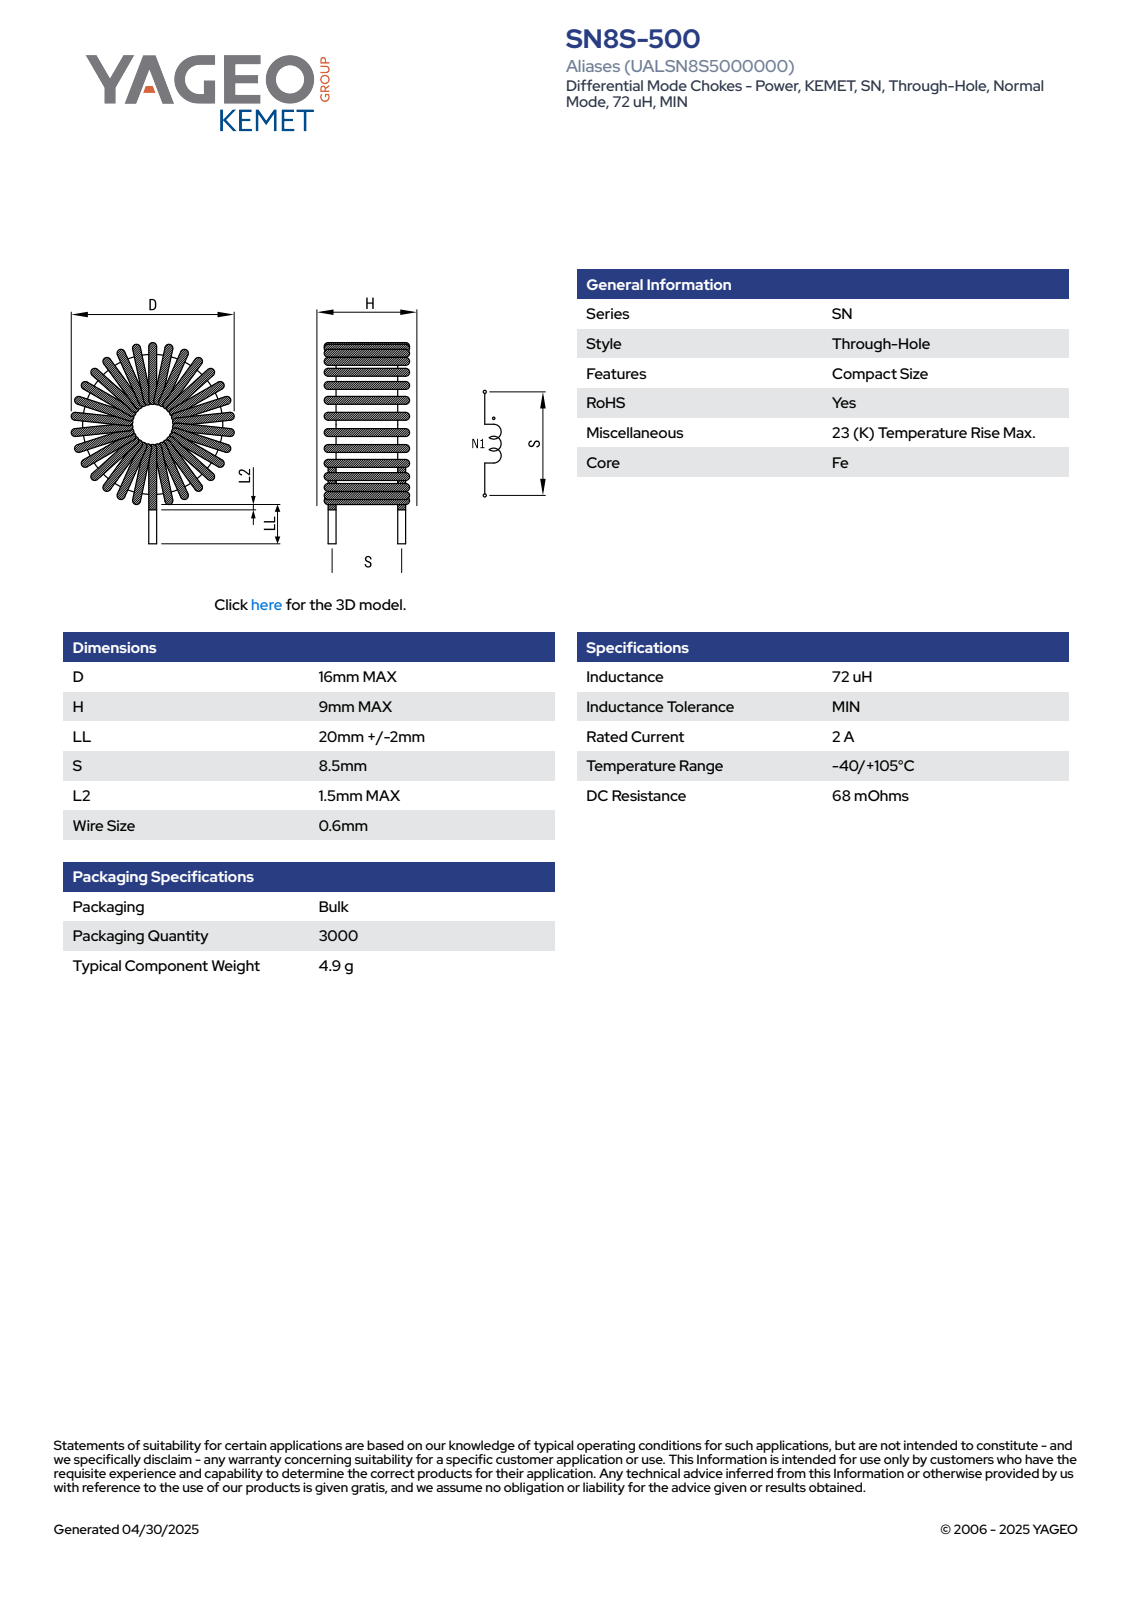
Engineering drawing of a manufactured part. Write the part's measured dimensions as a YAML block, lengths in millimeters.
part_name: "SN8S-500"
step_written_by: "SolidWorks 2018 (AUTOMOTIVE_DESIGN)"
units: millimeters
bodies: {solids: 1, faces: 77, planar: 12, cylindrical: 37, other: 28}
overall_size: [34.6, 16, 9.1]
volume: 1361
surface_area: 998
round_holes:
  - {diameter: 6.5, count: 1}
round_bosses_or_shafts:
  - {diameter: 0.6, count: 3}
  - {diameter: 16, count: 1}
partial_cylinders:
  - {radius: 0.3, count: 8}
  - {radius: 3.85, count: 1}
  - {radius: 6.6, count: 1}
  - {radius: 8, count: 1}
face_to_face_distances: [9, 1.8, 7.2, 5.4, 2.1, 6.9, 5.1, 4.8]
